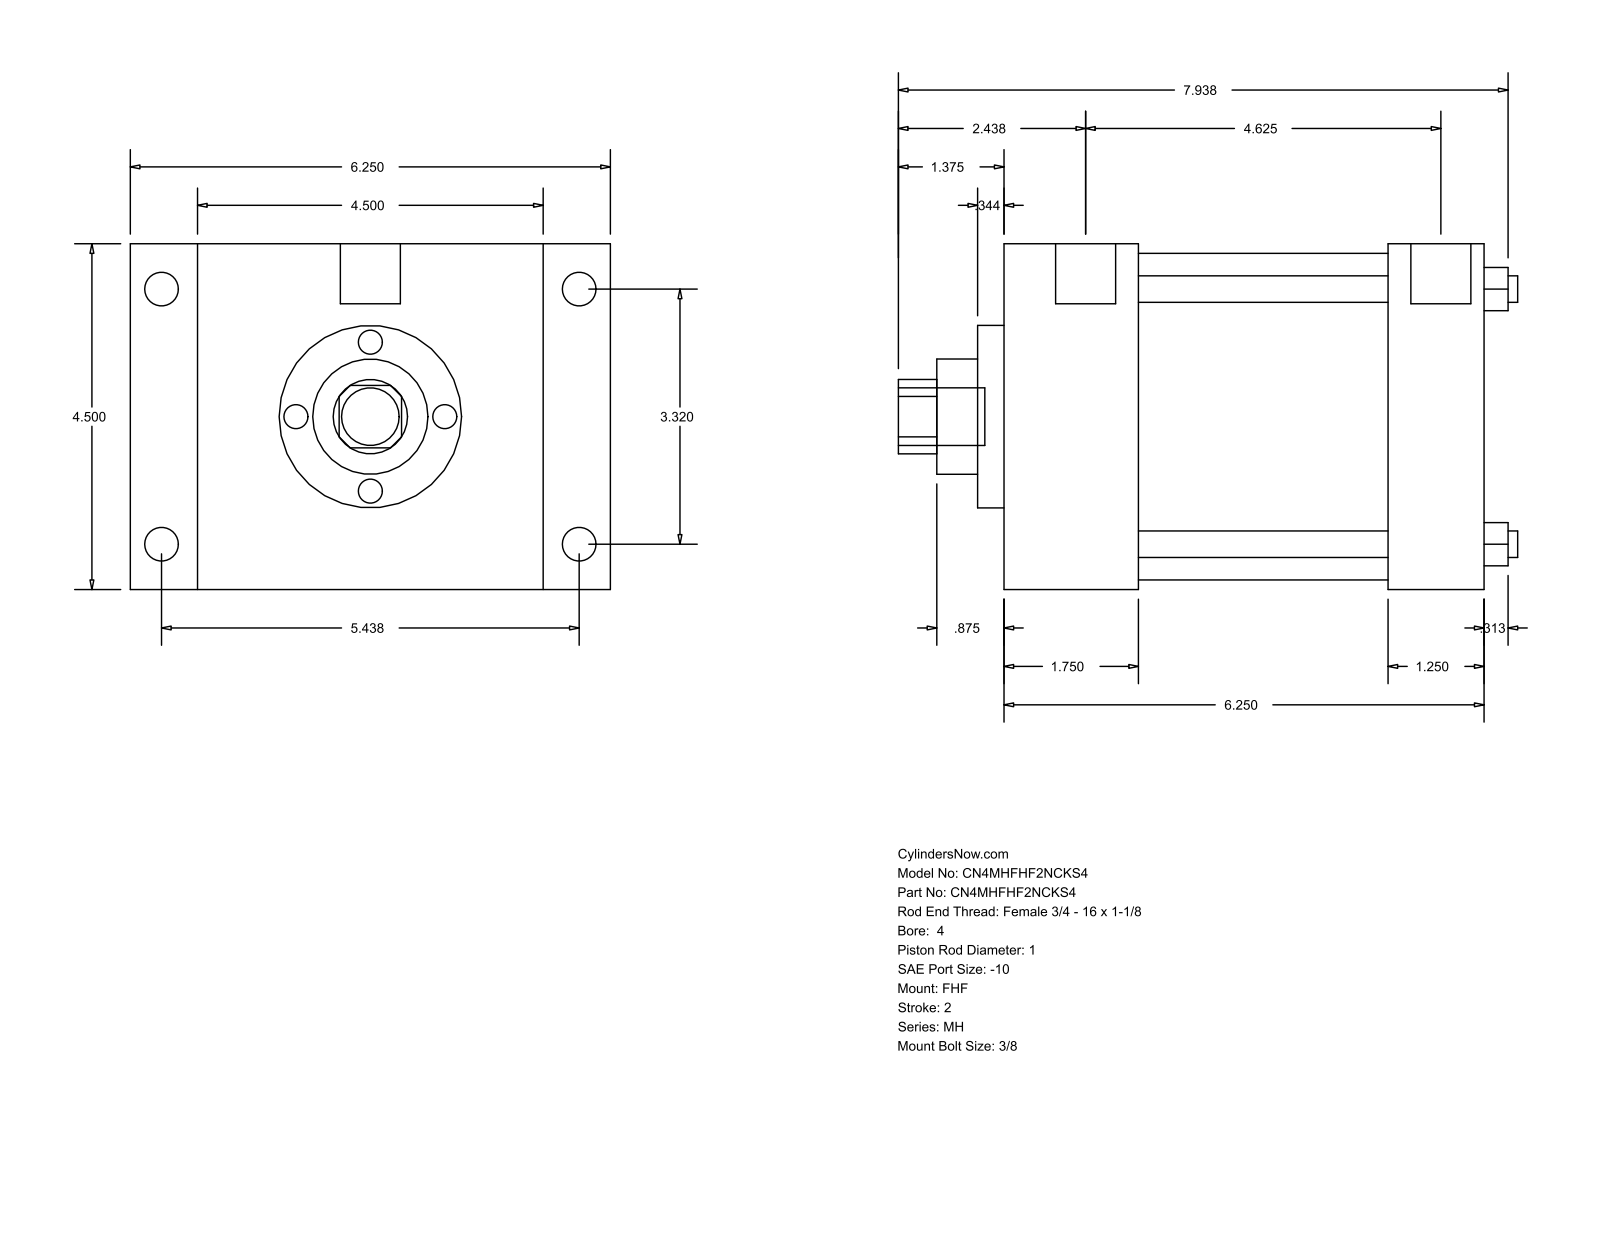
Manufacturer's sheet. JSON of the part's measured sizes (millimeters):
{"part_name": "MH_FHF__0400_1", "step_written_by": "GSSL Pune (CONFIG_CONTROL_DESIGN)", "units": "millimeters", "bodies": {"solids": 0, "faces": 90, "planar": 61, "cylindrical": 29, "other": 0}, "overall_size": [204.79, 158.75, 114.3], "round_holes": [[8.76, 4], [25.4, 1], [38.1, 1], [60.33, 1], [107.95, 1]], "round_bosses_or_shafts": [[11.13, 4], [8.73, 4], [19.84, 2], [19.05, 1]], "partial_cylinders_radius": [[12.29, 1]], "face_to_face_distances": [114.3, 158.76, 44.46, 22.23, 136.53, 127.01, 82.55, 31.75, 8.73, 53.19], "hole_center_spacings": [59.62, 84.32, 119.25]}
